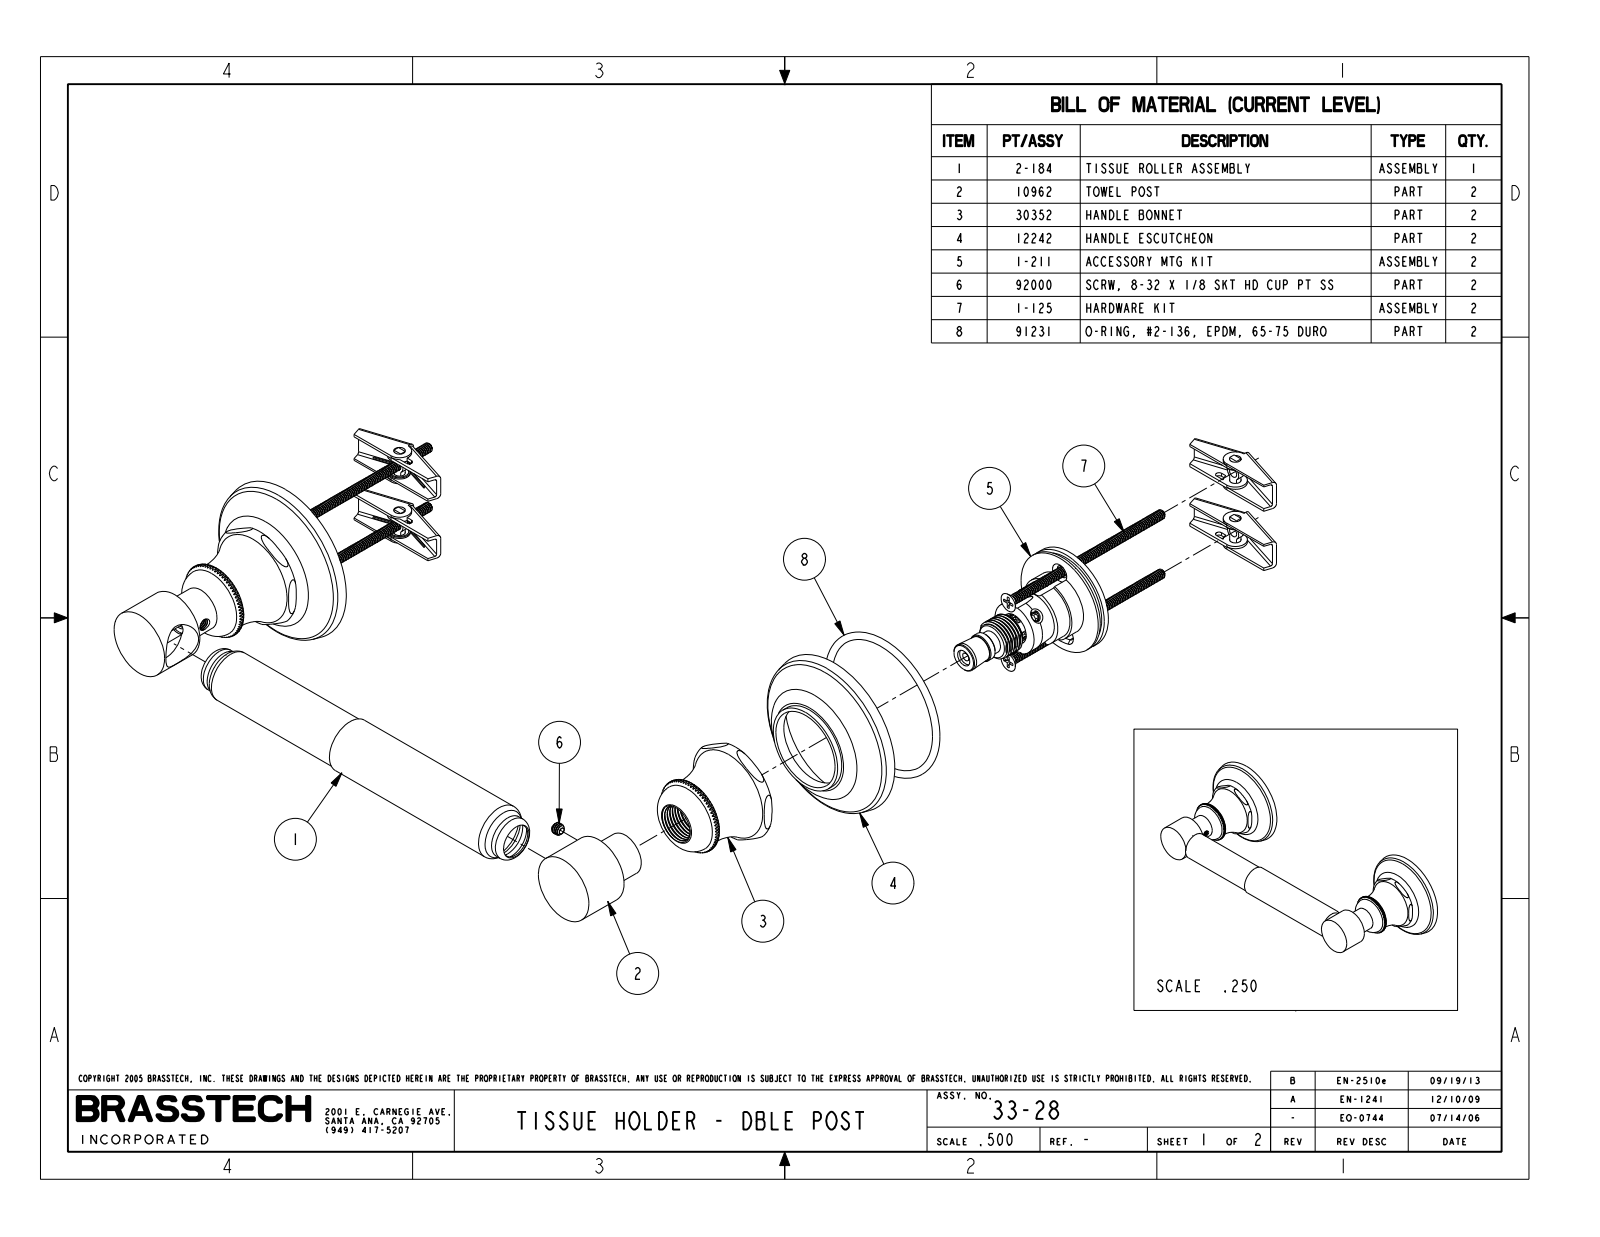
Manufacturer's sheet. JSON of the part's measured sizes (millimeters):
{"part_name": "33-28_WEB", "step_written_by": "PRO/ENGINEER BY PARAMETRIC TECHNOLOGY CORPORATION, 2009300 (CONFIG_CONTROL_DESIGN)", "units": "millimeters", "bodies": {"solids": 0, "faces": 166, "planar": 62, "cylindrical": 22, "other": 82}, "overall_size": [218.8, 74.3, 60.1], "round_holes": [[3.5, 1]], "round_bosses_or_shafts": [[24.9, 2], [15.9, 2], [20.3, 1], [19.1, 1]], "face_to_face_distances": [54.8, 54.8, 35.1, 79.4, 44.3, 114.4, 158.8, 89.3, 193.8, 54.2]}
